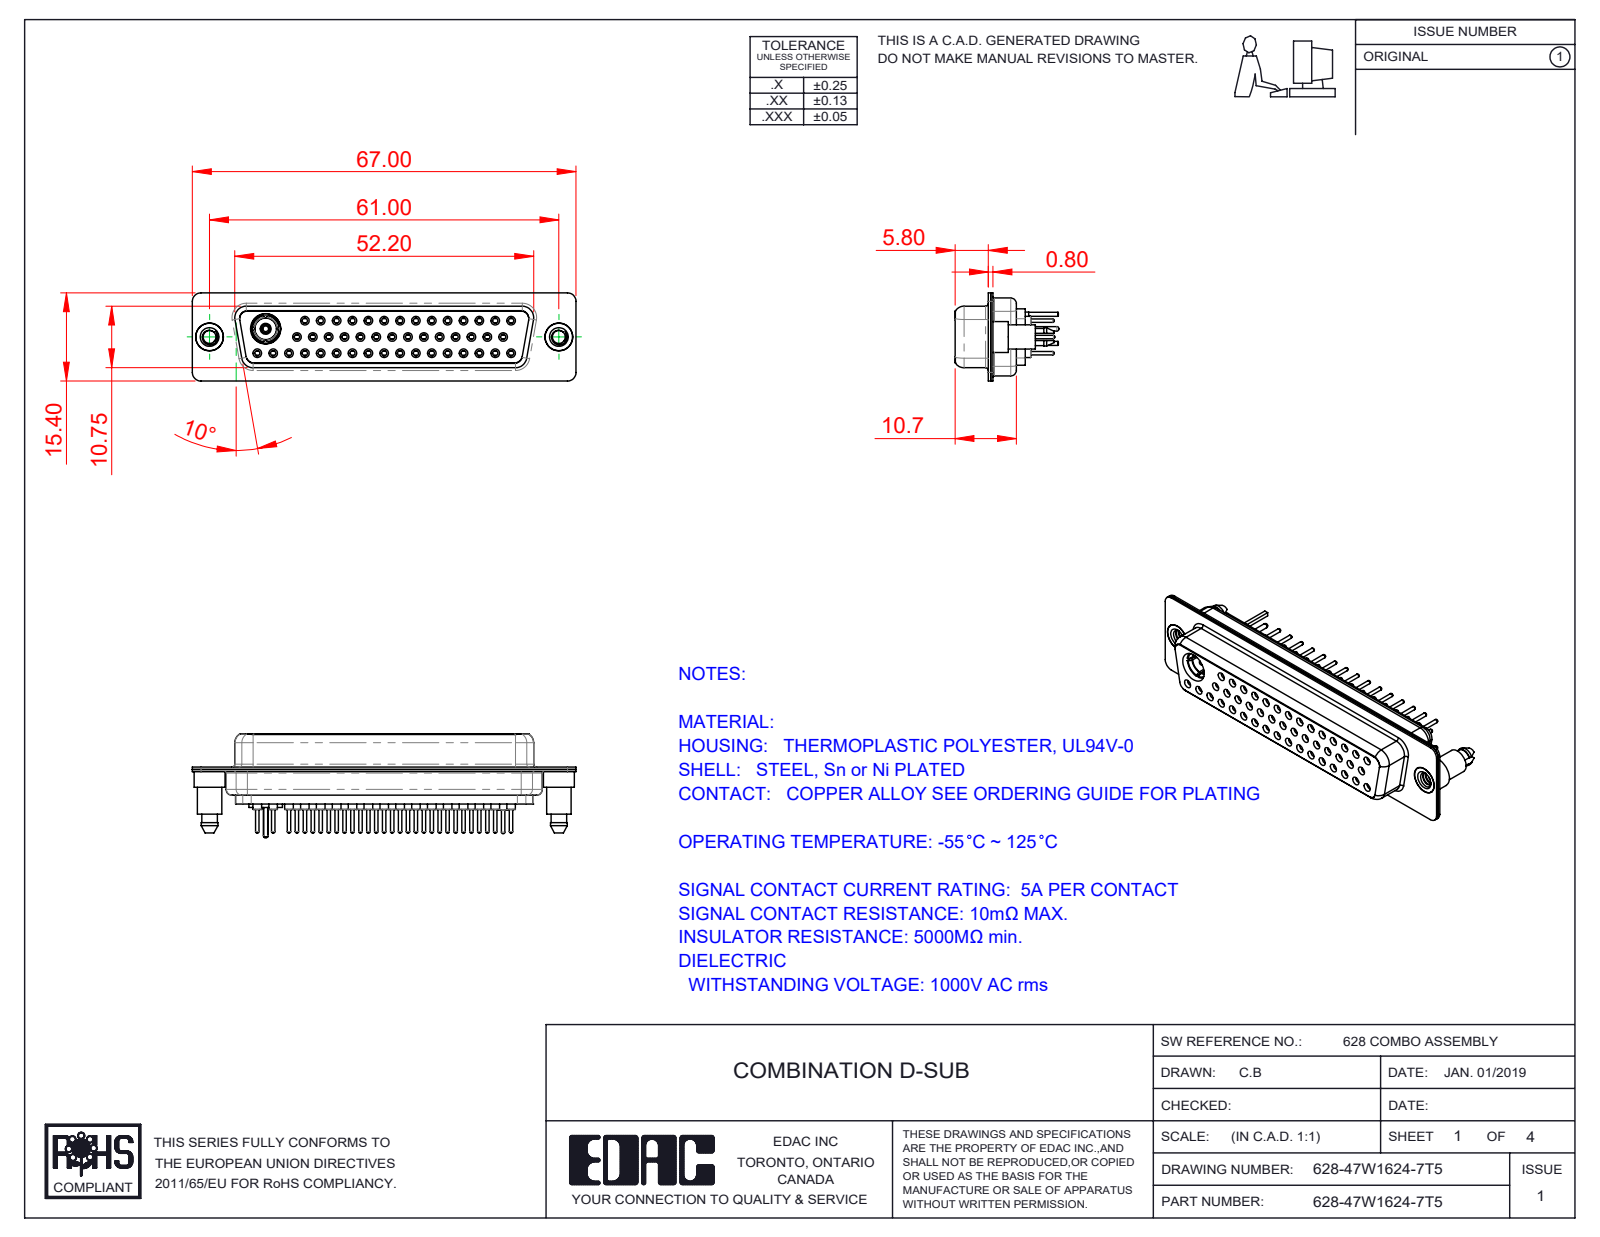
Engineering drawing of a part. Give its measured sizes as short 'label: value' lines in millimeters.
name: 628Combo Shell Rear_50 Contacts; Pin_Str; 628Combo Housing_47W1; Insulator Pin_Straight PC Tail (+8 more)
written by: SolidWorks 2016 (CONFIG_CONTROL_DESIGN)
unit: mm
bodies: 55 solids, 2973 faces (827 planar, 1080 cylindrical, 1066 other)
size: 67 × 18.15 × 15.4
volume: 7 178 mm³; area: 15 213 mm²
holes: 47× ⌀1.1, 46× ⌀1.5, 45× ⌀0.9, 45× ⌀2, 31× ⌀1.6, 14× ⌀1.7, 3× ⌀4.85, 2× ⌀2.26, 2× ⌀4, 2× ⌀4.05, 1× ⌀2.83, 1× ⌀3.3
bosses: 46× ⌀2.2, 46× ⌀0.6, 15× ⌀1.6, 2× ⌀5.4, 2× ⌀4.95, 2× ⌀4.8, 2× ⌀4.25, 1× ⌀5.85
rounds: 18× R1.5, 12× R1.35, 12× R2, 10× R1.6, 4× R0.25, 4× R0.5, 4× R0.6, 4× R0.65
face distances: 0.4, 6.05, 6.45, 11.33, 1.87, 12.25, 6.2, 5.8, 10.35, 10.93
hole spacings: 3.16, 2.77, 5.54, 8.31, 11.08, 13.85, 16.62, 19.39
